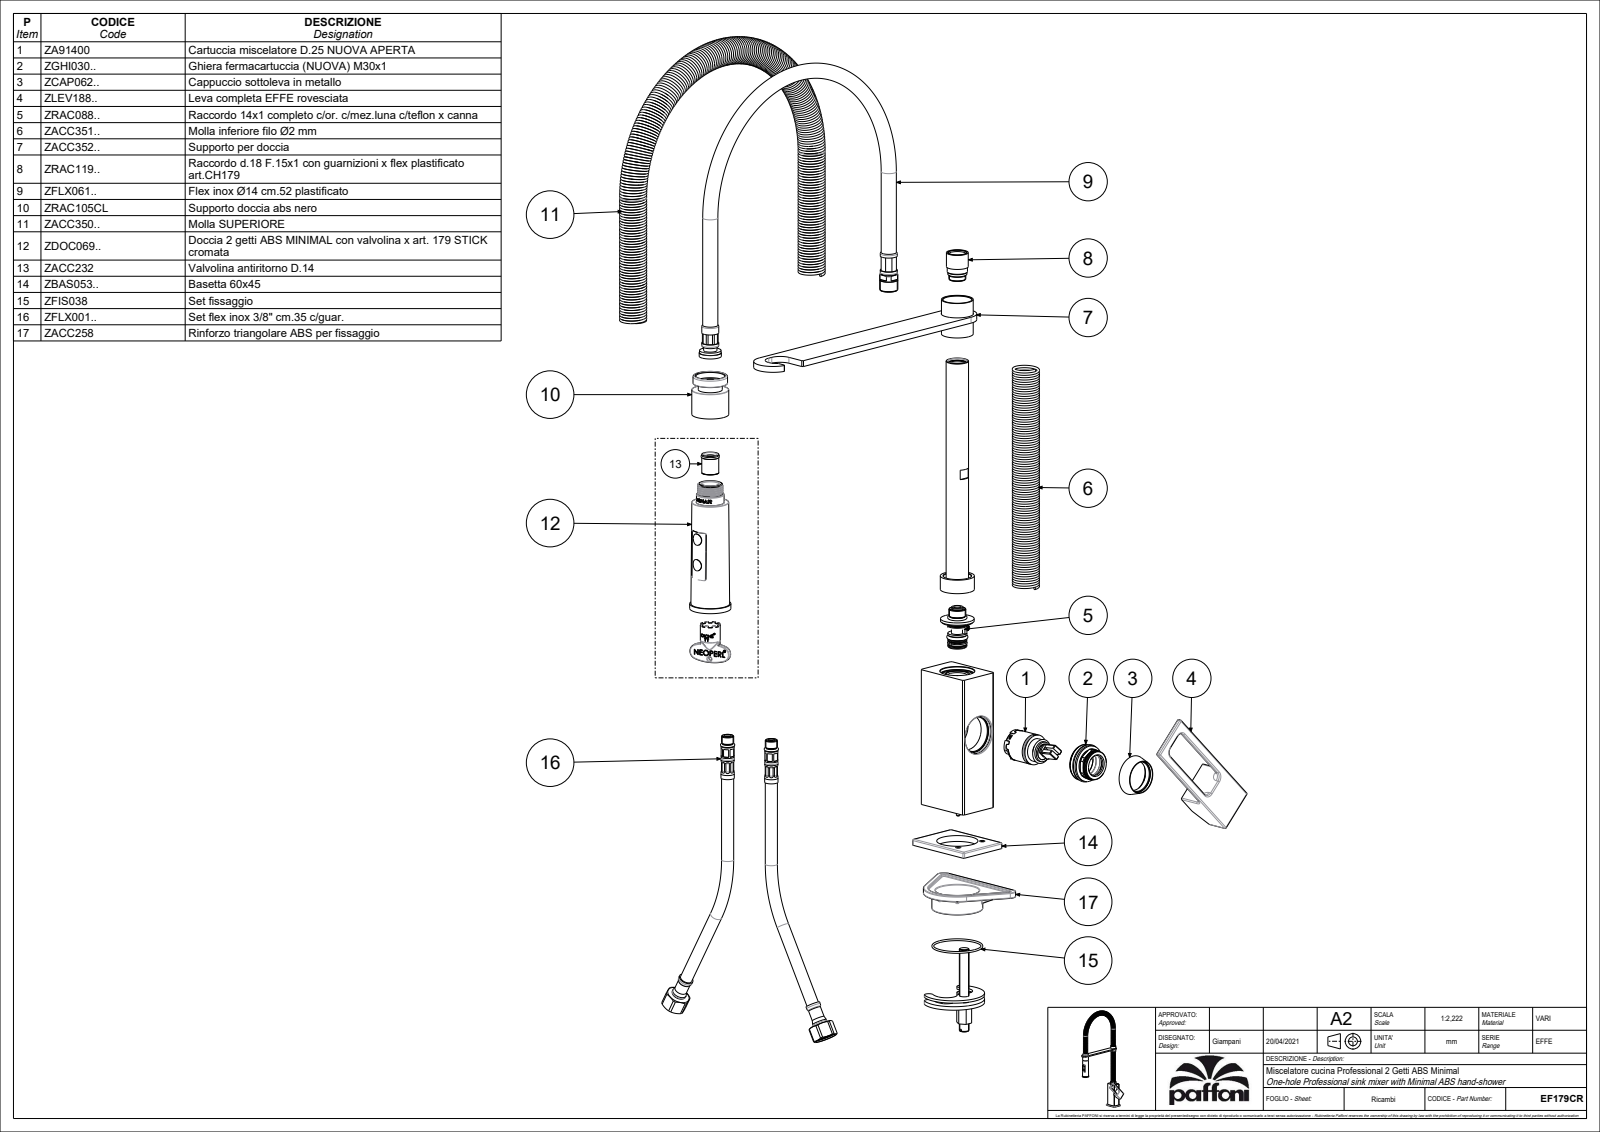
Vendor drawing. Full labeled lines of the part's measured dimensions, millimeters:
Part name (STEP PRODUCT): EF179CR
STEP written by: CREO PARAMETRIC BY PTC INC, 2020044 (CONFIG_CONTROL_DESIGN)
Units: millimetres
Bodies: 4 solids, 2716 faces (923 planar, 1019 cylindrical, 774 other)
Overall size (bounding box): 536.87 × 256.24 × 83.28
Volume: 355 660 mm³ · Surface area: 253 798 mm²
Round holes (diameter × count): ⌀0.5 ×172, ⌀3 ×2, ⌀5 ×2, ⌀5.5 ×2, ⌀6 ×2, ⌀9 ×2, ⌀9.9 ×2, ⌀11 ×2, ⌀23 ×2, ⌀4 ×1, ⌀4.5 ×1, ⌀5.2 ×1
Round bosses / shafts (diameter × count): ⌀0.7 ×16, ⌀9.5 ×2, ⌀7.6 ×2, ⌀38.8 ×1, ⌀34 ×1, ⌀31.5 ×1, ⌀30.5 ×1, ⌀28.75 ×1
Partial cylindrical surfaces — rounded edges, fillets, slot ends (radius × count): R0.5 ×75, R1 ×50, R0.25 ×34, R0.3 ×23, R0.7 ×10, R0.2 ×9, R1.5 ×8, R0.8 ×6
Main face-to-face distances: 5, 36, 50, 9, 310, 28.28, 41, 78.28, 315, 35.99
Hole centre spacings: 7.87, 0.69, 0.7, 1.39, 5.02, 5.53, 7.1, 7.23
